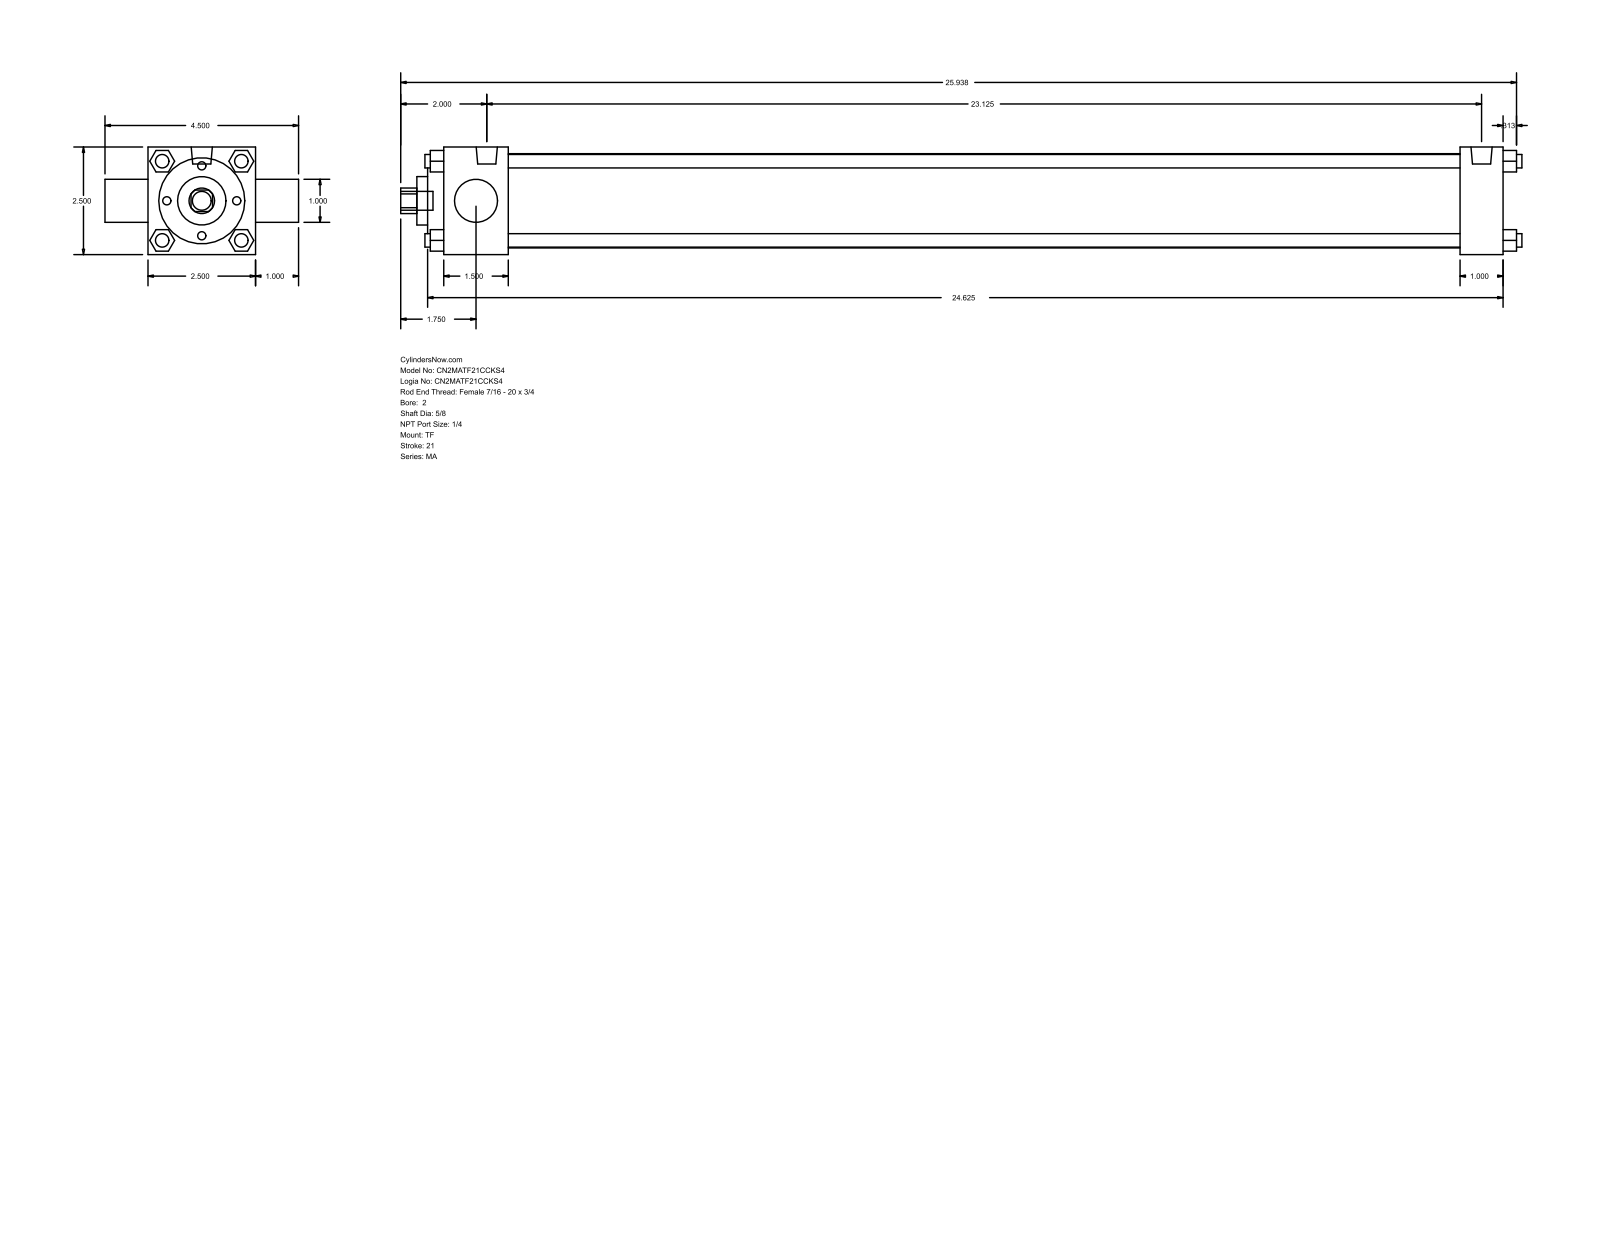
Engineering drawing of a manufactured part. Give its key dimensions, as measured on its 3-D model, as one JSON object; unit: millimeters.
{"part_name": "MA_TF__0200_0.625", "step_written_by": "GSSL Pune (CONFIG_CONTROL_DESIGN)", "units": "millimeters", "bodies": {"solids": 0, "faces": 122, "planar": 93, "cylindrical": 29, "other": 0}, "overall_size": [661.99, 114.3, 63.5], "round_holes": [[15.88, 1], [25.4, 1], [28.57, 1], [50.8, 1], [55.63, 1]], "round_bosses_or_shafts": [[7.94, 7], [12.49, 2], [11.11, 1]], "partial_cylinders_radius": [[7.54, 1]], "face_to_face_distances": [63.5, 25.4, 38.1, 12.7, 625.48, 9.52, 600.08, 561.98, 587.38, 47.62]}
